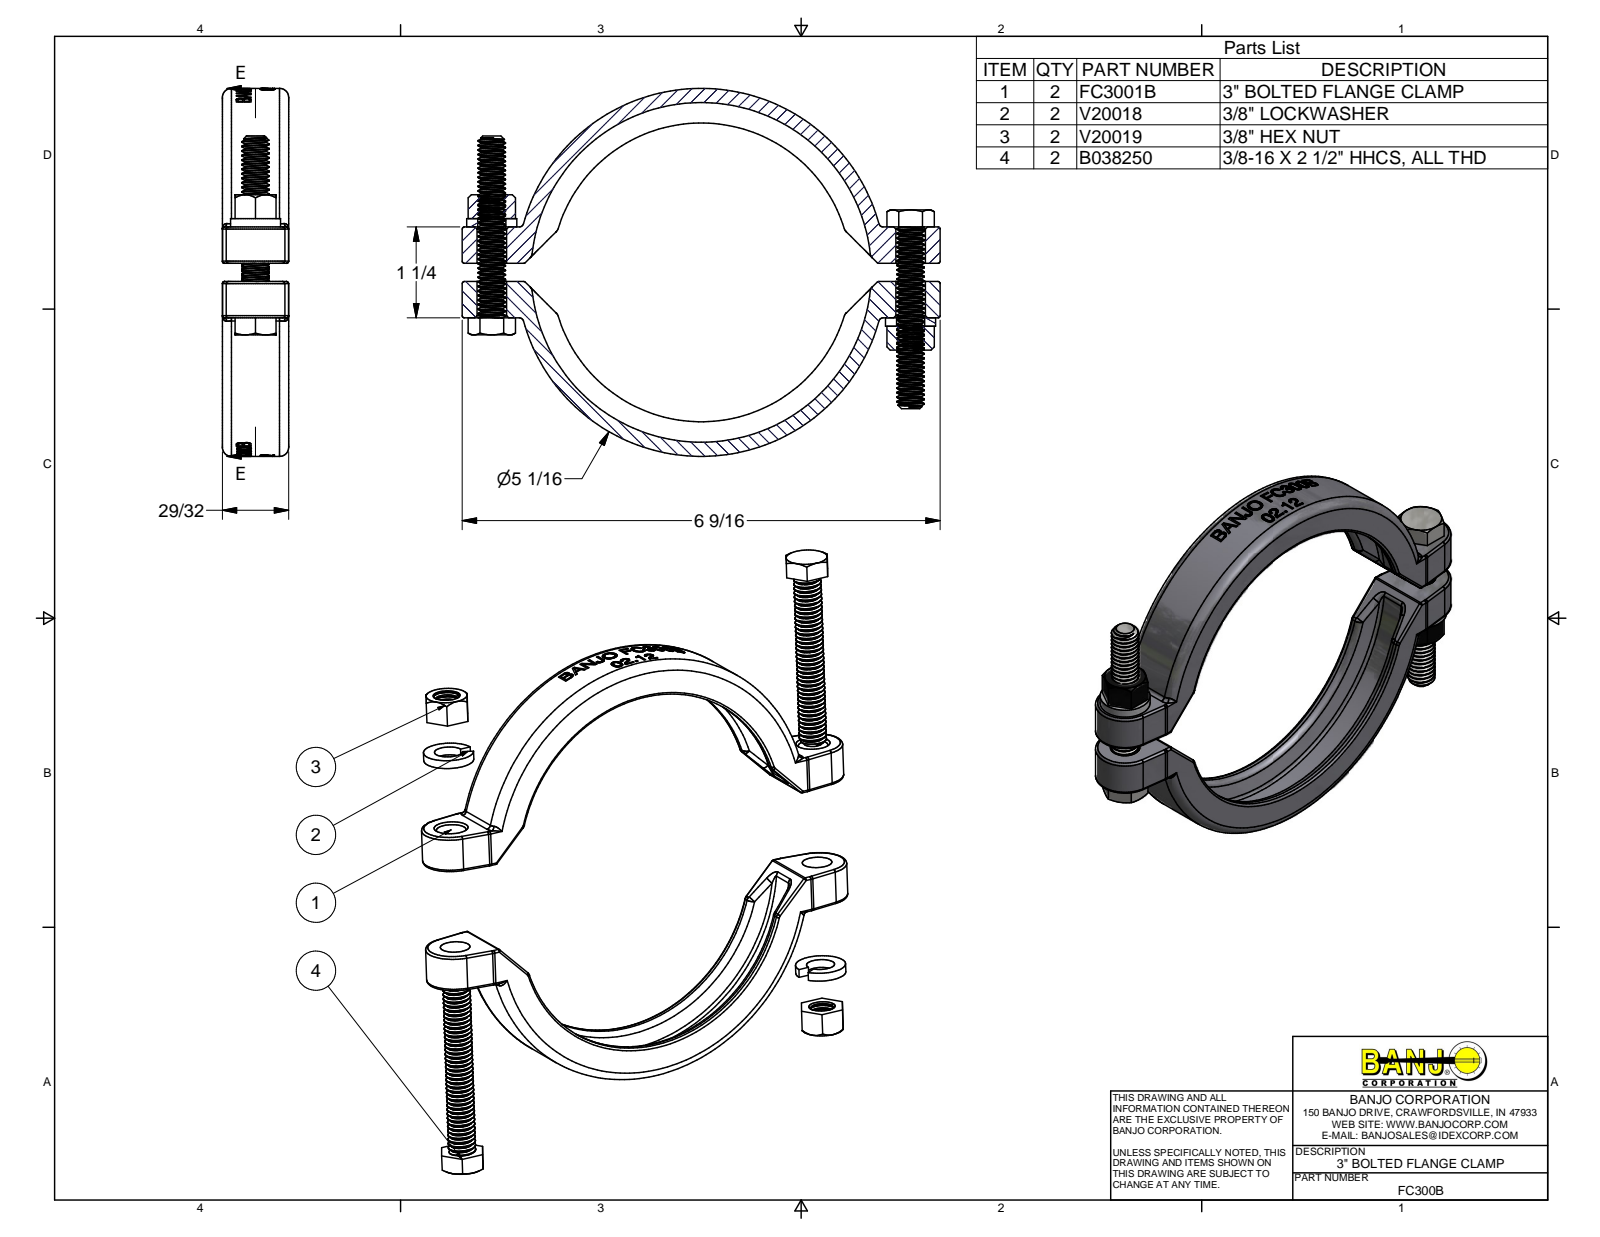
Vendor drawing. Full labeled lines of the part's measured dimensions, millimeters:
Part name (STEP PRODUCT): FC3001B; V20010; V20018; V20019 (+1 more)
STEP written by: Autodesk Inventor 2014 (AUTOMOTIVE_DESIGN)
Units: millimetres
Bodies: 8 solids, 1098 faces (212 planar, 322 cylindrical, 564 other)
Overall size (bounding box): 166.69 × 128.52 × 23.11
Volume: 90 610 mm³ · Surface area: 40 343 mm²
Round holes (diameter × count): ⌀10.32 ×3, ⌀7.81 ×2, ⌀9.78 ×2, ⌀104.34 ×1, ⌀118.62 ×1
Round bosses / shafts (diameter × count): ⌀8.24 ×30, ⌀17.46 ×2, ⌀9.52 ×2, ⌀128.52 ×1
Partial cylindrical surfaces — rounded edges, fillets, slot ends (radius × count): R0.76 ×36, R2.29 ×8, R1.52 ×4, R4.12 ×4, R6.35 ×4, R10.32 ×3, R8.12 ×2, R64.01 ×1
Main face-to-face distances: 23.12, 19.04, 12.7, 14.28, 6.34, 2.93, 15.63, 21.97, 34.67, 19.05
Hole centre spacings: 146.04, 146.05
